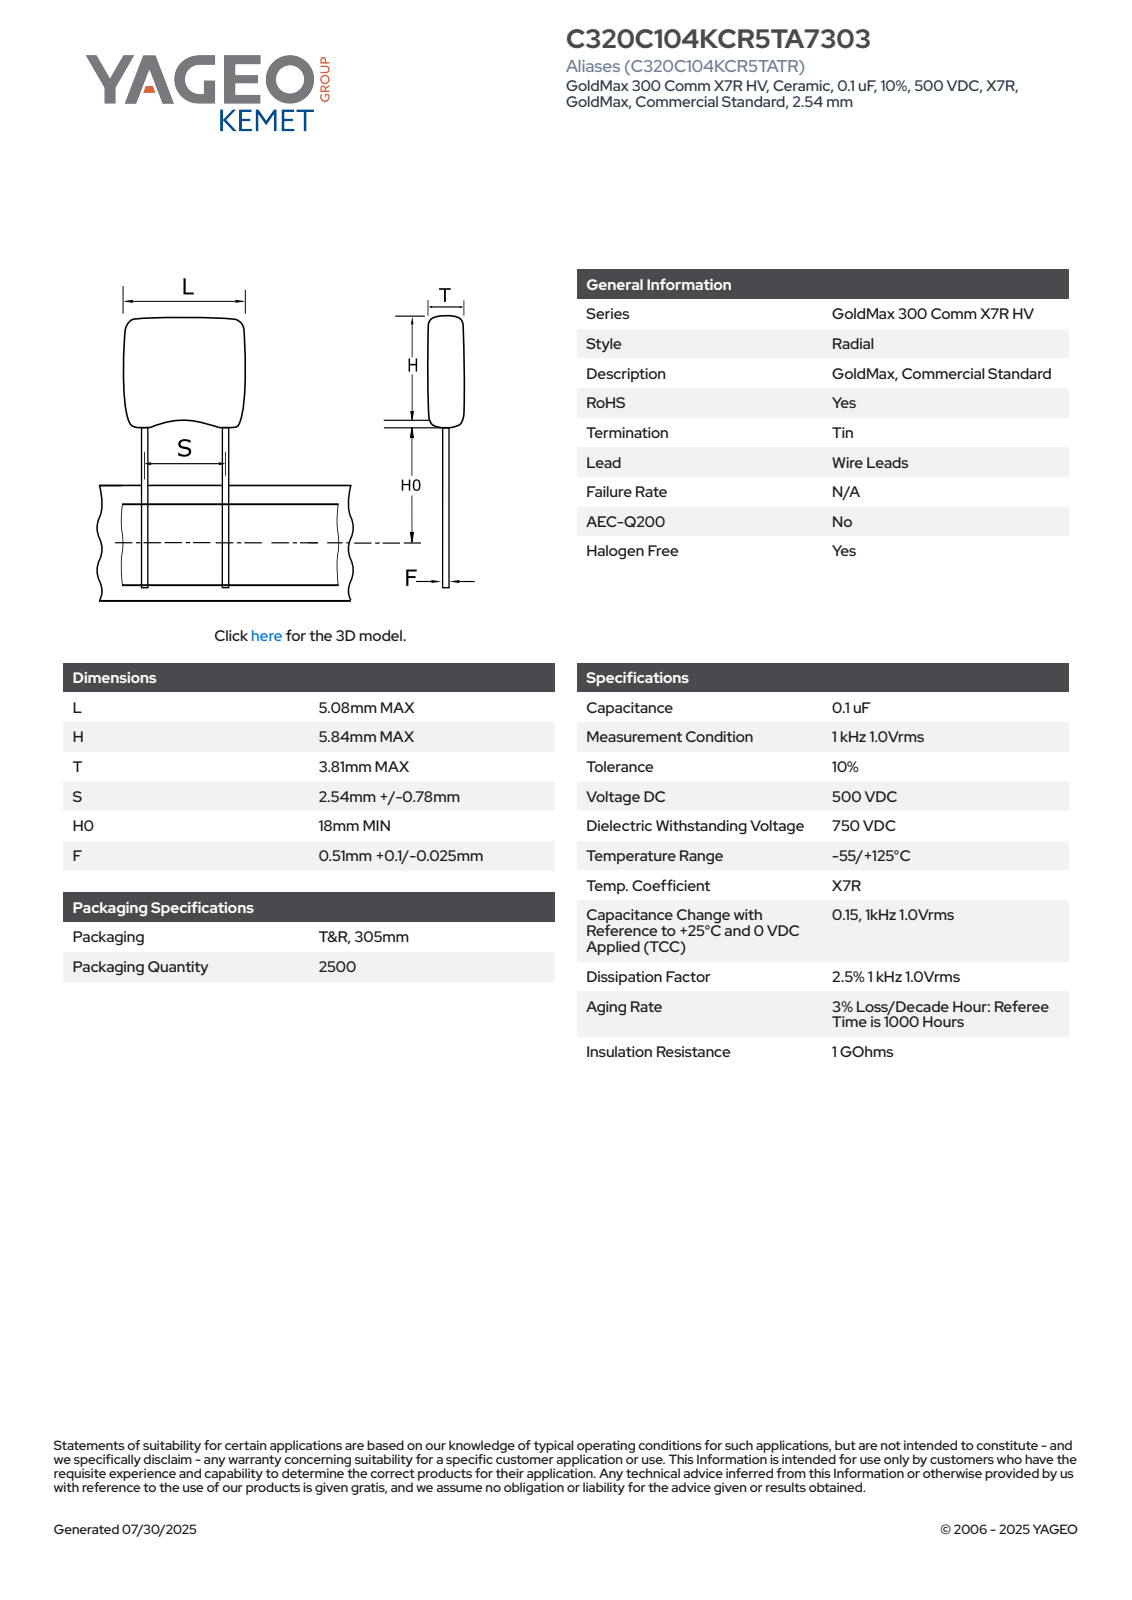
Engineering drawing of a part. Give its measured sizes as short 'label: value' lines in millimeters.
name: CCR_KRCST_5.08X5.84_L5.08H5.84T3.81S2.54H018F0.61
written by: SolidWorks 2014 (AUTOMOTIVE_DESIGN)
unit: mm
bodies: 4 solids, 83 faces (65 planar, 14 cylindrical, 4 other)
size: 24.51 × 5.08 × 3.81
volume: 130 mm³; area: 207 mm²
bosses: 2× ⌀0.61
rounds: 10× R0.75
face distances: 3.81, 5.08, 6.51, 18, 24.51, 0.54, 21.43, 3.43, 3.08, 20.89
